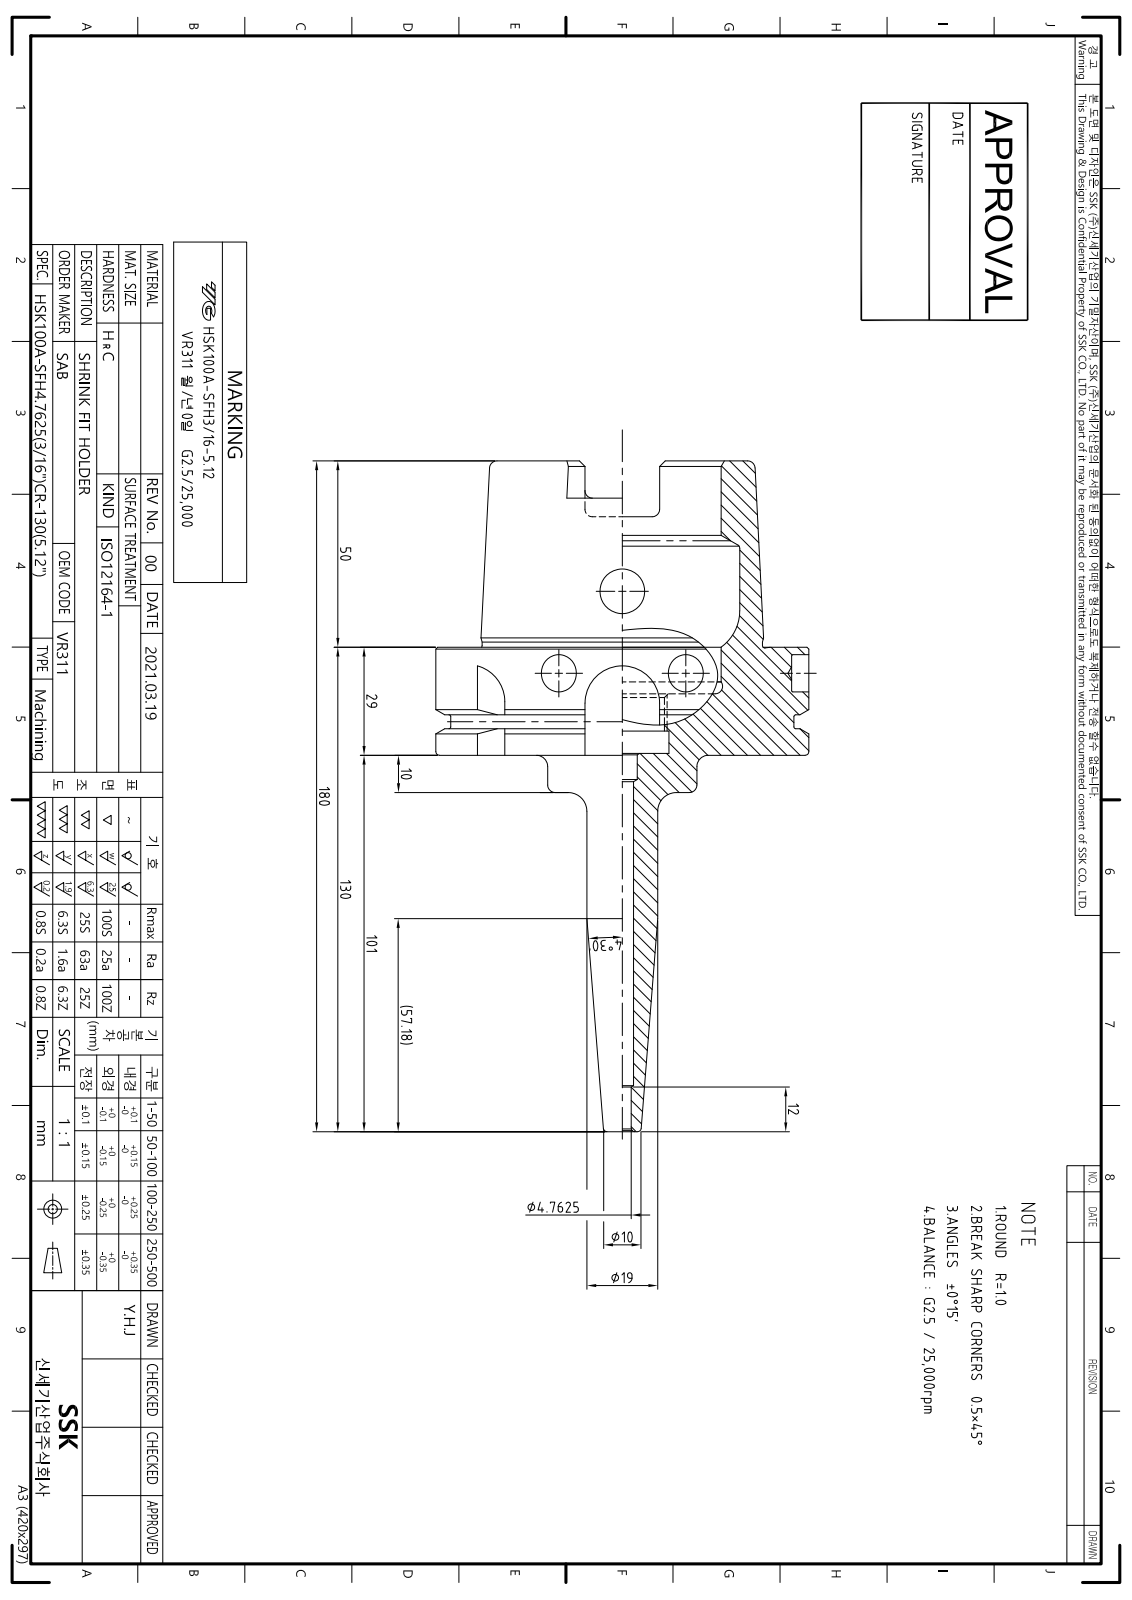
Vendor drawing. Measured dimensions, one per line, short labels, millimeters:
name: LO-HSK100A-SFH4.7625-130
written by: Autodesk Inventor 2022 (AUTOMOTIVE_DESIGN)
unit: mm
bodies: 1 solid, 117 faces (37 planar, 35 cylindrical, 45 other)
size: 180 × 100 × 100
volume: 283 683 mm³; area: 56 835 mm²
holes: 1× ⌀4.76, 1× ⌀6, 1× ⌀8, 1× ⌀10, 1× ⌀12, 1× ⌀22.38, 1× ⌀25, 1× ⌀53, 1× ⌀63
bosses: 1× ⌀100, 1× ⌀92, 1× ⌀75.41, 1× ⌀40, 1× ⌀19
rounds: 6× R2, 4× R4.88, 4× R10
face distances: 29, 12.5, 16.5, 79, 62.5, 50, 10, 78.5, 28.5, 16
